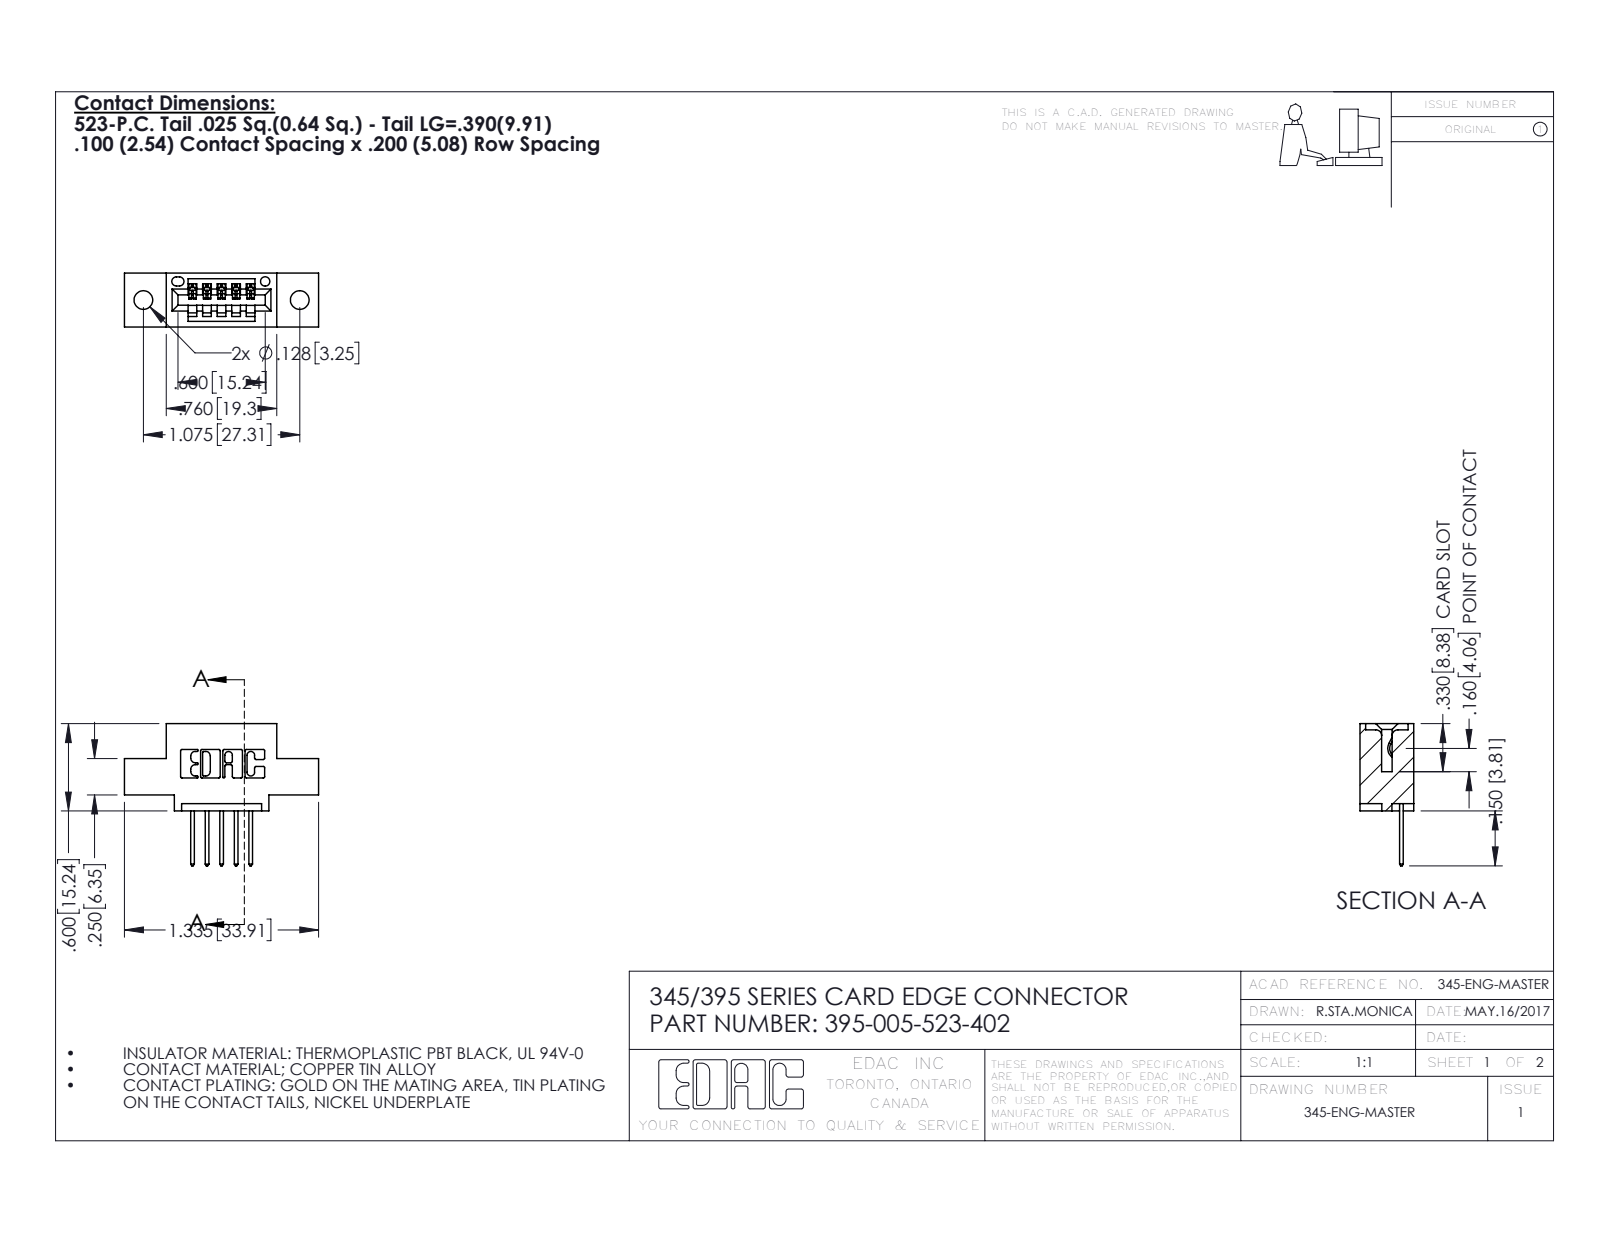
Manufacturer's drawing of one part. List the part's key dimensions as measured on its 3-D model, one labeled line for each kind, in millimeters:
Part name (STEP PRODUCT): 345-292-001_345-293-123; 395-005-523-402; 345 Part_0.110 Offset - 0.128 Dia
STEP written by: SolidWorks 2016 (CONFIG_CONTROL_DESIGN)
Units: millimetres
Bodies: 6 solids, 420 faces (284 planar, 136 cylindrical, 0 other)
Overall size (bounding box): 33.9 × 24.8 × 9.4
Volume: 2 800 mm³ · Surface area: 3 041 mm²
Round holes (diameter × count): ⌀3.3 ×2, ⌀1.6 ×1
Partial cylindrical surfaces — rounded edges, fillets, slot ends (radius × count): R0.3 ×22, R0.2 ×10, R0.3 ×10, R0.2 ×6, R0.8 ×6, R0.7 ×3, R0.8 ×2, R1 ×2
Main face-to-face distances: 5.1, 9.4, 7.6, 1.8, 2.5, 0.6, 6.4, 2.5, 6.9, 1.5
Hole centre spacings: 6.9, 21.5, 27.3
